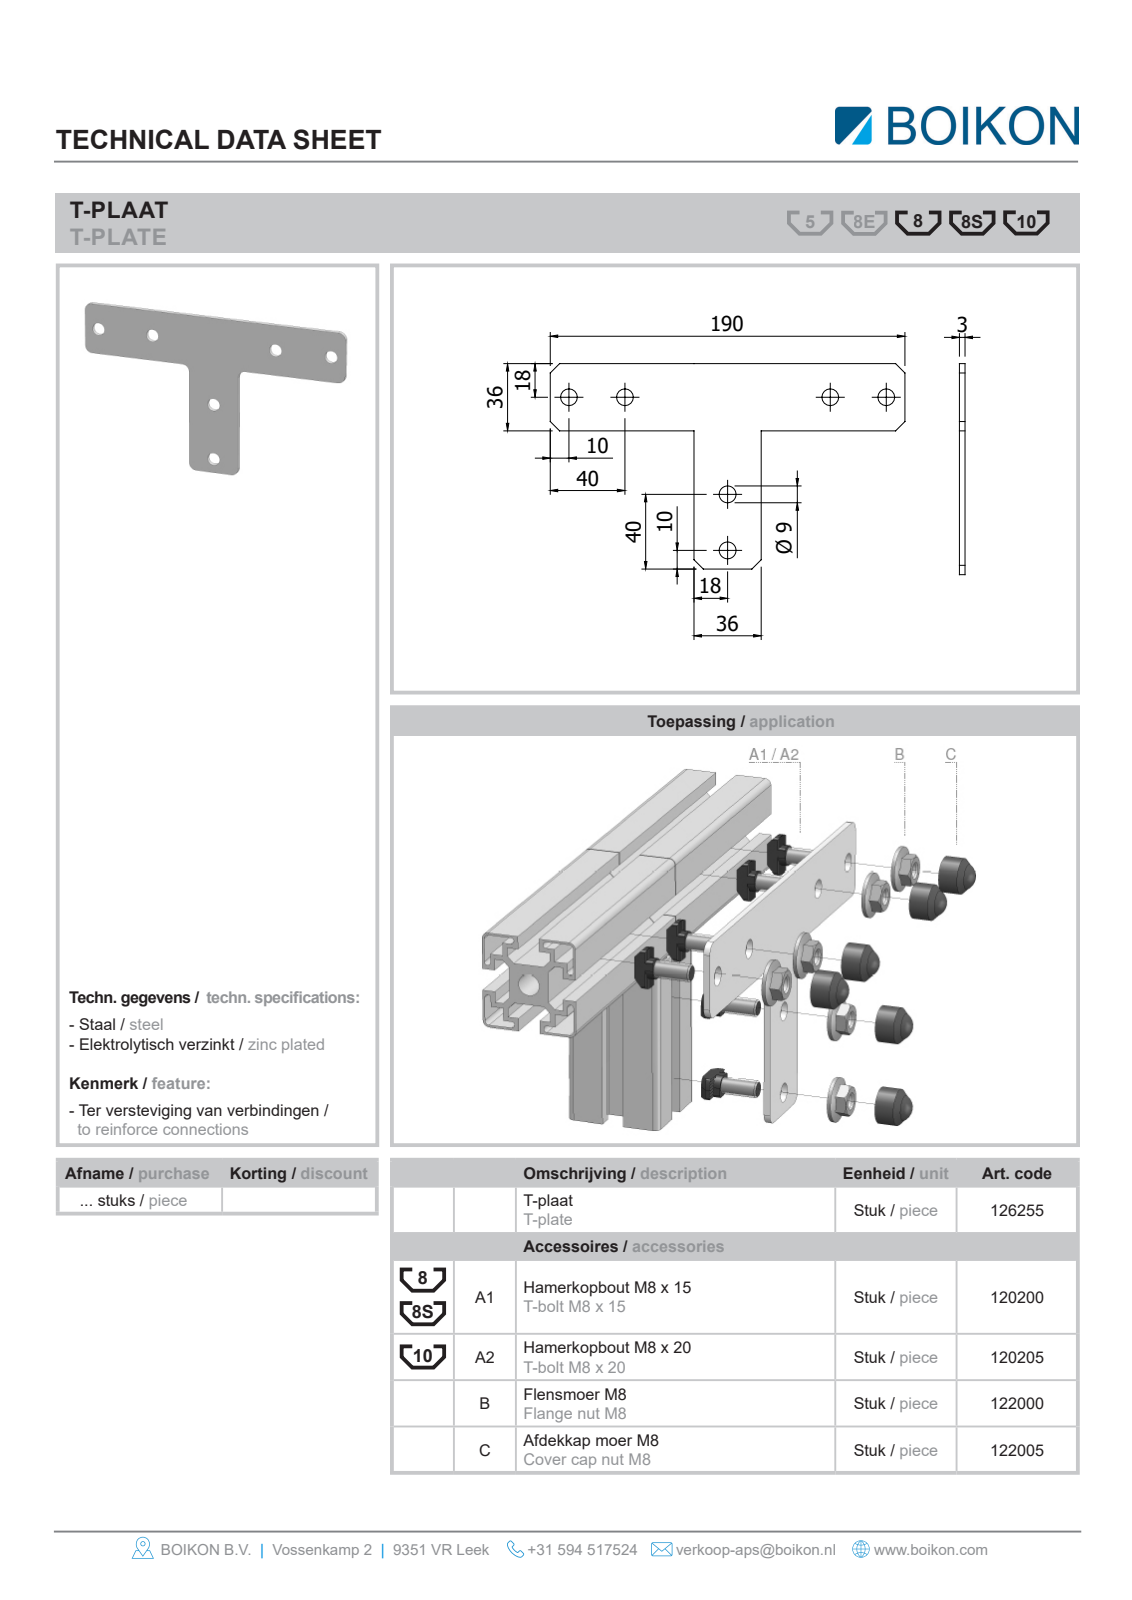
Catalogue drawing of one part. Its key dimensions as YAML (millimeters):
part_name: "Root; 126255 T-plaatBOIKON; 122000Flensmoer M8BOIKON; 122005Afdekkap voor moer M8BOIKON (+1 more)"
step_written_by: "HiCAD 2013 1802.4 Build 509 (AUTOMOTIVE_DESIGN)"
units: millimeters
bodies: {solids: 19, faces: 552, planar: 376, cylindrical: 98, other: 78}
overall_size: [191, 113.5, 30.8]
volume: 56905
surface_area: 41278
round_holes:
  - {diameter: 8, count: 6}
  - {diameter: 9, count: 6}
round_bosses_or_shafts:
  - {diameter: 21, count: 6}
  - {diameter: 16.8, count: 6}
  - {diameter: 6.47, count: 6}
partial_cylinders:
  - {radius: 1, count: 30}
  - {radius: 5, count: 20}
  - {radius: 1.16, count: 6}
  - {radius: 9.5, count: 6}
face_to_face_distances: [3, 13, 7, 11.5, 5.5, 10, 4.5, 34.64, 24.5, 10.3]
hole_center_spacings: [96.18, 40, 63.64, 120.21, 130, 90, 170]
